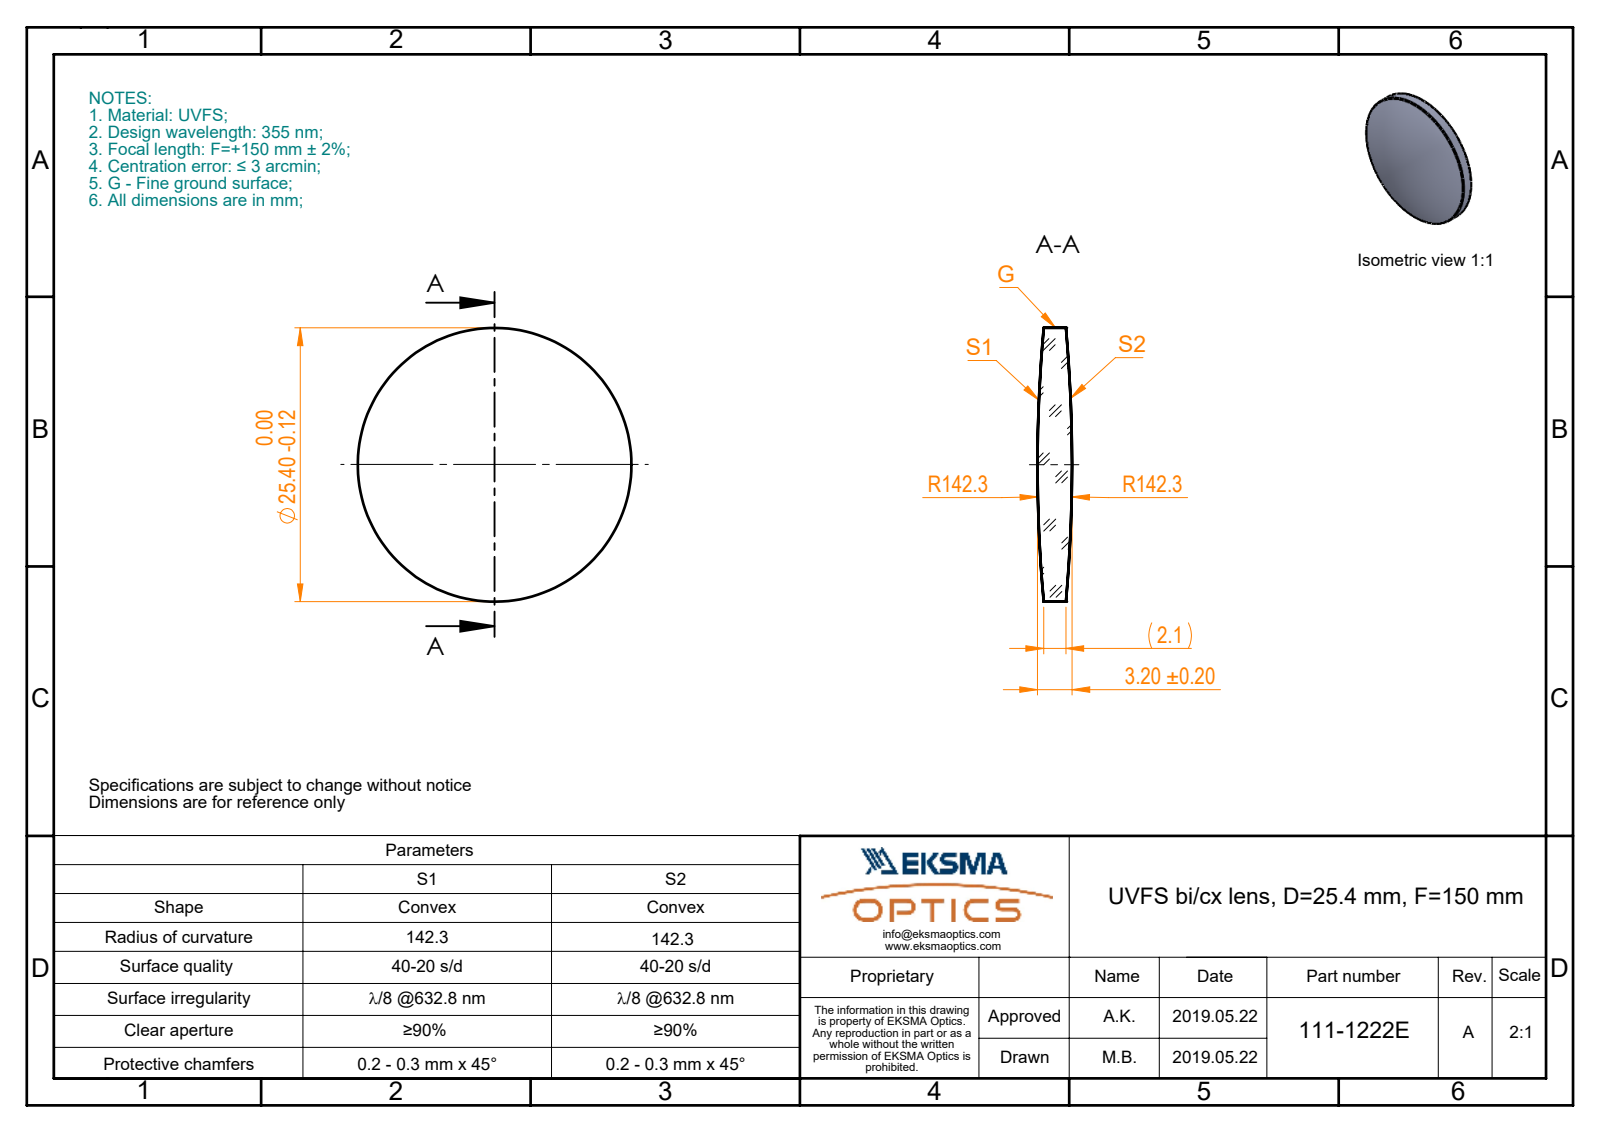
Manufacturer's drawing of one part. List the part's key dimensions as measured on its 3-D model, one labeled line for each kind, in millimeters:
Part name (STEP PRODUCT): 111-1222E UVFS bi-cx 25.4 F150
STEP written by: SolidWorks 2017 (CONFIG_CONTROL_DESIGN)
Units: millimetres
Bodies: 1 solid, 6 faces (0 planar, 2 cylindrical, 4 other)
Overall size (bounding box): 25.4 × 25.4 × 3.2
Volume: 1 334 mm³ · Surface area: 1 180 mm²
Round bosses / shafts (diameter × count): ⌀25.4 ×1
